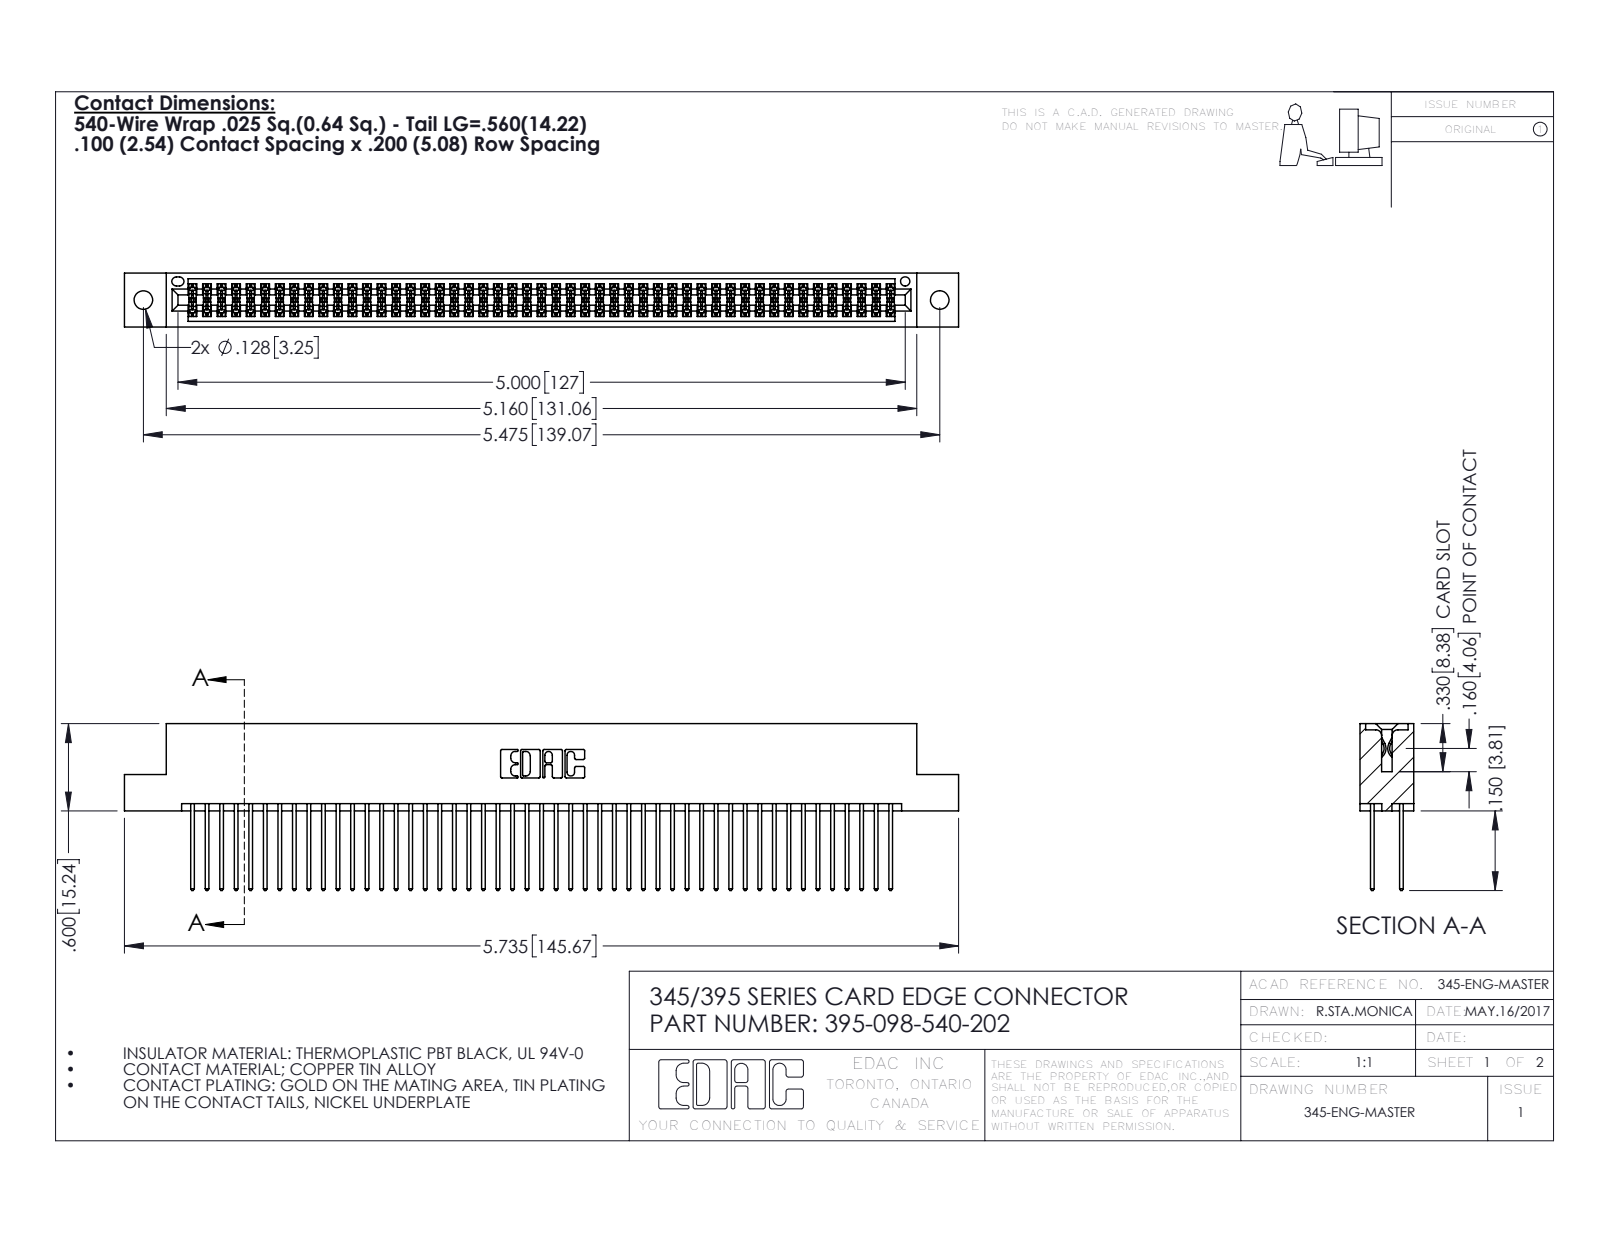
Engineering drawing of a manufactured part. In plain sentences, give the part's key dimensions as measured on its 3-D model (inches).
The part is named "345-292-001_345-293-140; 345 Part_Flush Mounting Lugs - 0.128 Dia; 395-098-540-202". Its 3-D file was written by "SolidWorks 2016 (CONFIG_CONTROL_DESIGN)". It is 99 solids with 5026 faces: 3314 planar, 1712 cylindrical and 0 other. Overall it measures 5.735 by 1.147 by 0.37 inches. Its volume is 0.888 cubic inches and its surface area 35.8 square inches. Round holes: 2 of diameter 0.128, 1 of diameter 0.064. Partial cylindrical surfaces (rounded edges, fillets, slot ends): 147 of radius 0.006, 98 of radius 0.01, 22 of radius 0.01, 6 of radius 0.007, 6 of radius 0.031, 3 of radius 0.026, 2 of radius 0.014, 2 of radius 0.019. The main face-to-face distances are 0.298, 0.072, 0.2, 0.098, 0.272, 0.025, 0.37, 0.225, 0.175, 0.149. The hole center spacings are 0.27, 5.239, 5.475.
